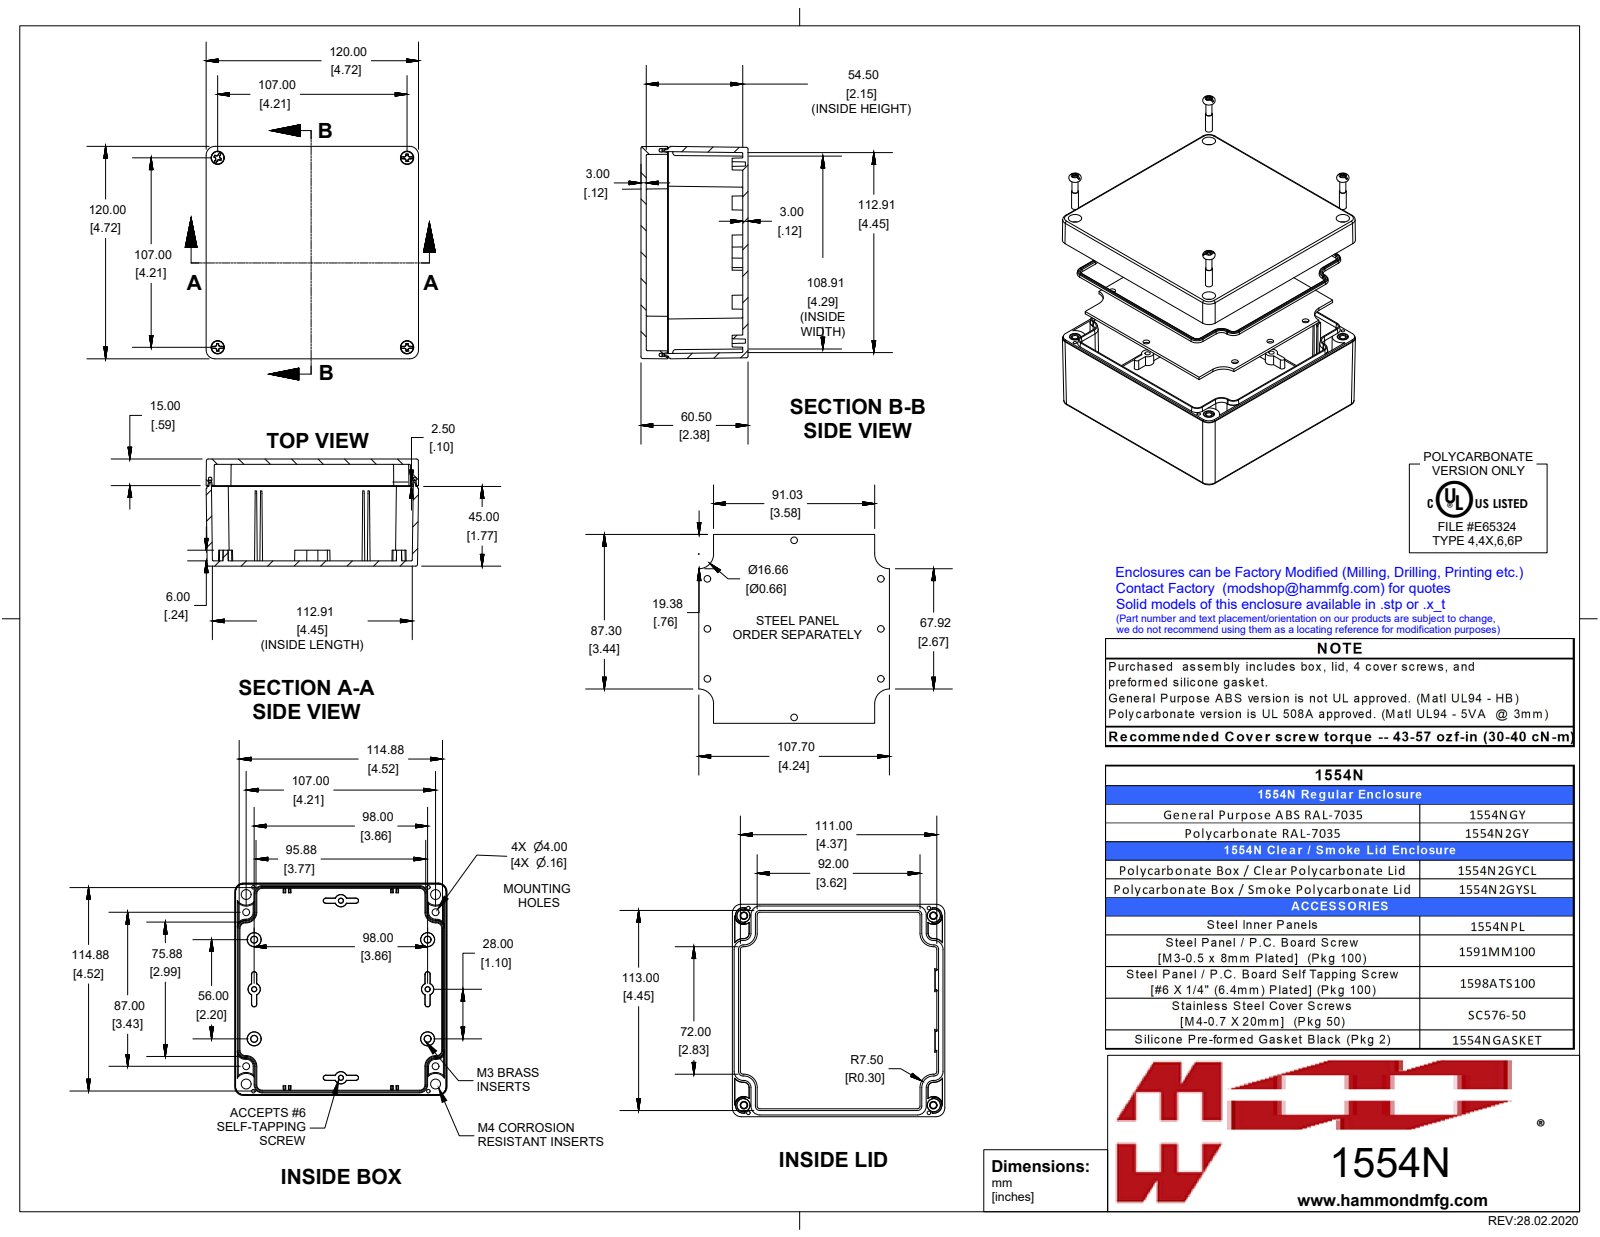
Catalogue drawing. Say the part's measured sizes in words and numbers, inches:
The part is named "1554NGY". Its 3-D file was written by "SolidWorks 2019 (AUTOMOTIVE_DESIGN)". It is 16 solids with 1384 faces: 394 planar, 346 cylindrical and 644 other. Overall it measures 4.724 by 4.724 by 2.382 inches. Its volume is 12.39 cubic inches and its surface area 244.6 square inches. Round holes: 8 of diameter 0.079, 4 of diameter 0.097, 4 of diameter 0.11, 4 of diameter 0.128, 4 of diameter 0.138, 4 of diameter 0.147. Round bosses or shafts: 4 of diameter 0.25, 4 of diameter 0.218, 4 of diameter 0.21, 4 of diameter 0.19, 4 of diameter 0.154, 4 of diameter 0.153, 4 of diameter 0.15, 4 of diameter 0.135. Partial cylindrical surfaces (rounded edges, fillets, slot ends): 52 of radius 0.02, 8 of radius 0.039, 8 of radius 0.197, 4 of radius 0.328, 2 of radius 0.059. The main face-to-face distances are 0.118, 2.264, 2.382, 0.354, 1.909, 0.236, 2.146, 2.028, 0.419, 0.3. The hole center spacings are 3.858, 2.111, 0.197, 1.019, 1.102, 1.154, 1.177, 2.031.
